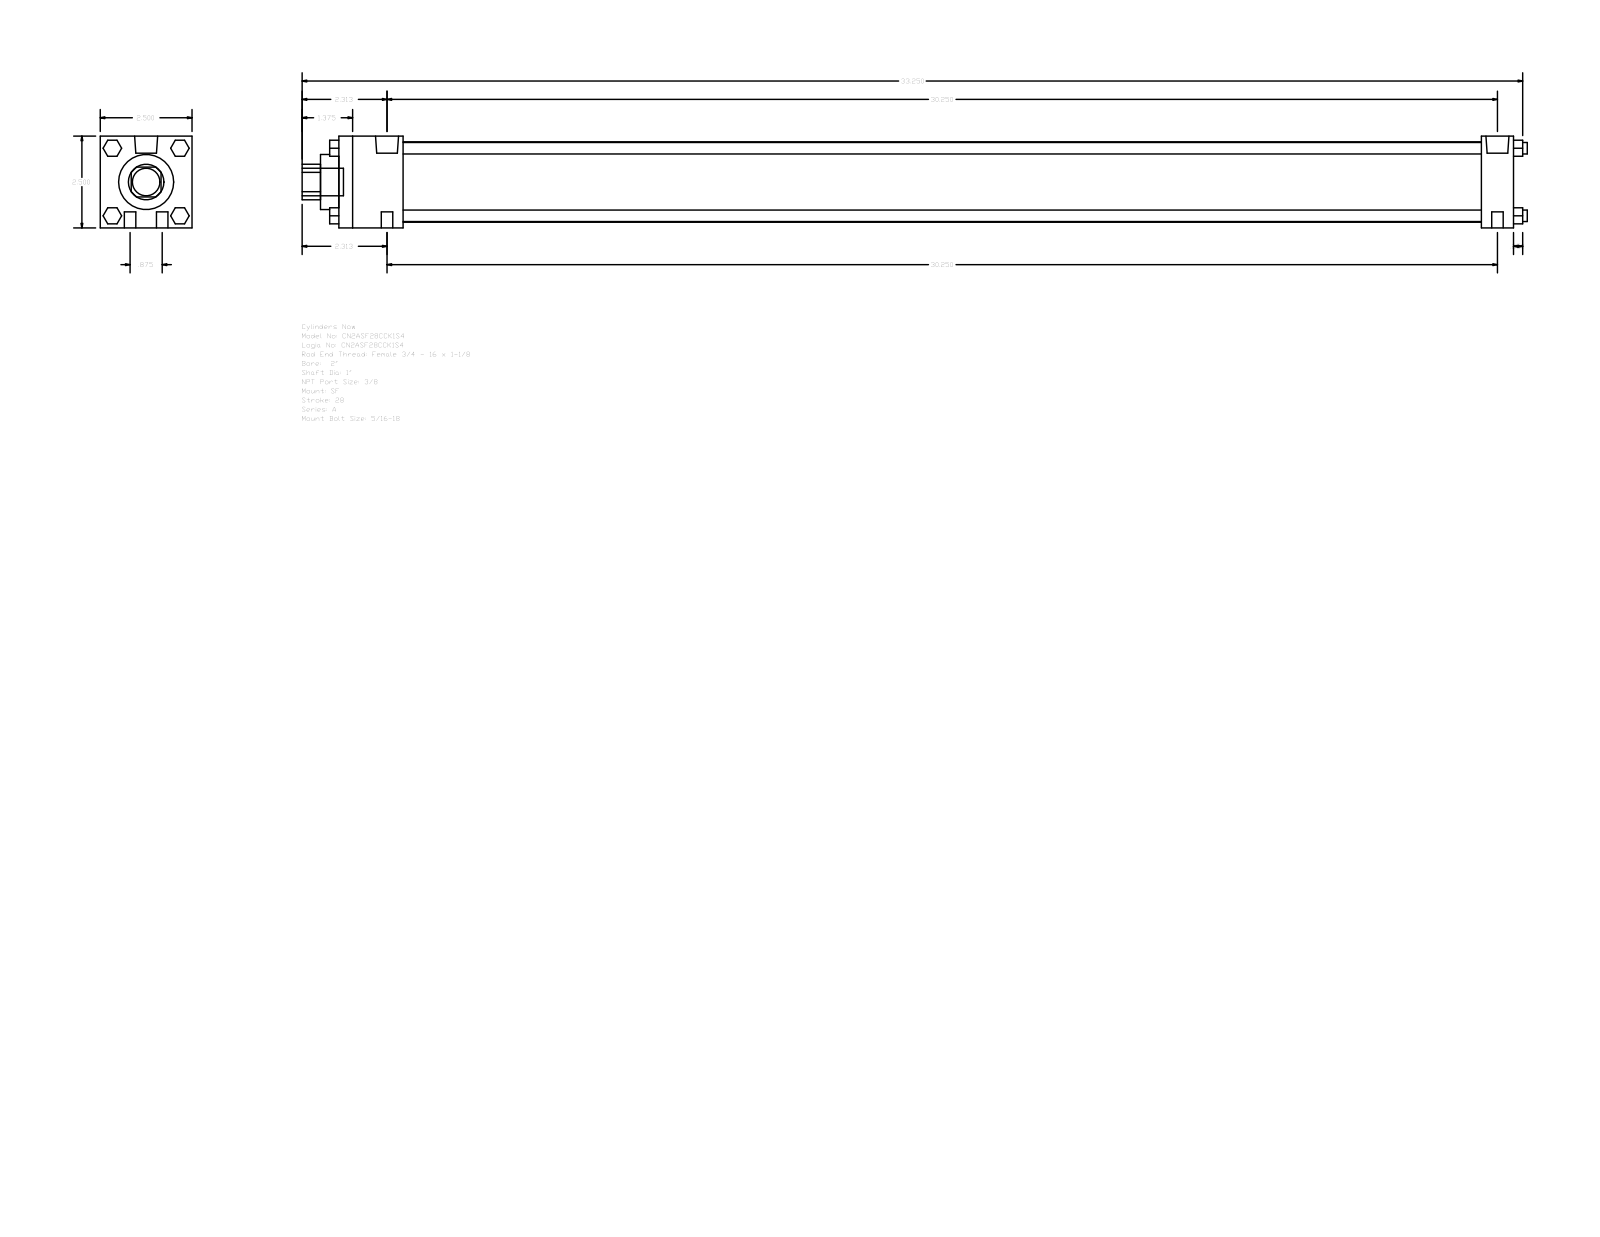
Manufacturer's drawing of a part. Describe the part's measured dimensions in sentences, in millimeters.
The part is named "A_SF__0200_1". Its 3-D file was written by "GSSL Pune (CONFIG_CONTROL_DESIGN)". It is 0 solids with 124 faces: 94 planar, 30 cylindrical and 0 other. Overall it measures 847.73 by 63.5 by 63.5 millimeters. Round holes: 1 of diameter 25.4, 1 of diameter 38.1, 1 of diameter 55.63. Round bosses or shafts: 8 of diameter 7.94, 2 of diameter 15.93, 2 of diameter 5.56, 1 of diameter 19.05. Partial cylindrical surfaces (rounded edges, fillets, slot ends): 1 of radius 12.29. The main face-to-face distances are 63.5, 812.8, 790.58, 22.22, 44.45, 746.13, 768.35, 12.7, 825.5, 6.35.
